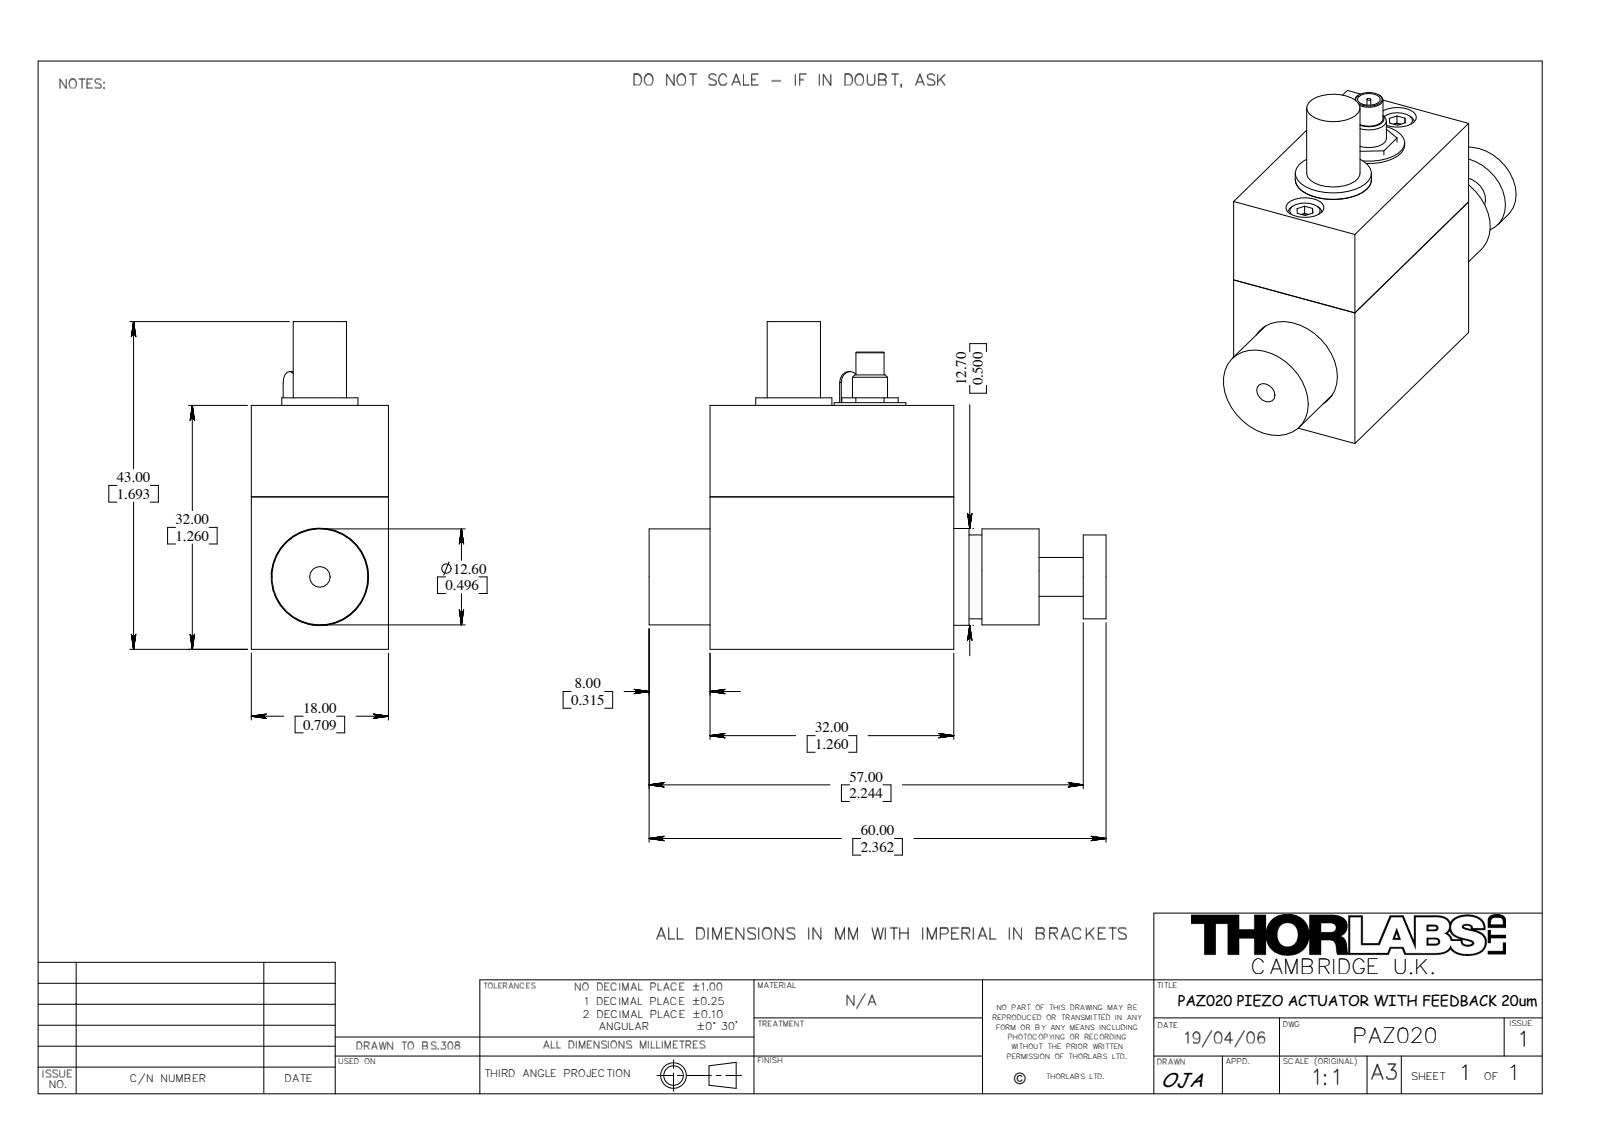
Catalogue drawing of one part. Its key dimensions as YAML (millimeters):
part_name: "15663-E0W"
step_written_by: "SolidWorks 2007 (AUTOMOTIVE_DESIGN)"
units: millimeters
bodies: {solids: 0, faces: 126, planar: 72, cylindrical: 42, other: 12}
overall_size: [60, 43, 18]
round_holes:
  - {diameter: 2.5, count: 2}
  - {diameter: 5, count: 2}
  - {diameter: 2.71, count: 1}
  - {diameter: 3, count: 1}
  - {diameter: 5.3, count: 1}
  - {diameter: 12.8, count: 1}
round_bosses_or_shafts:
  - {diameter: 12.6, count: 1}
  - {diameter: 11, count: 1}
  - {diameter: 10, count: 1}
  - {diameter: 9.4, count: 1}
  - {diameter: 9, count: 1}
  - {diameter: 7, count: 1}
  - {diameter: 5.1, count: 1}
  - {diameter: 4.6, count: 1}
partial_cylinders:
  - {radius: 1.5, count: 2}
  - {radius: 1.44, count: 1}
face_to_face_distances: [18, 32, 20, 40, 8, 12, 11.2, 43.2, 51.2, 8.8]
hole_center_spacings: [8, 18, 26]
